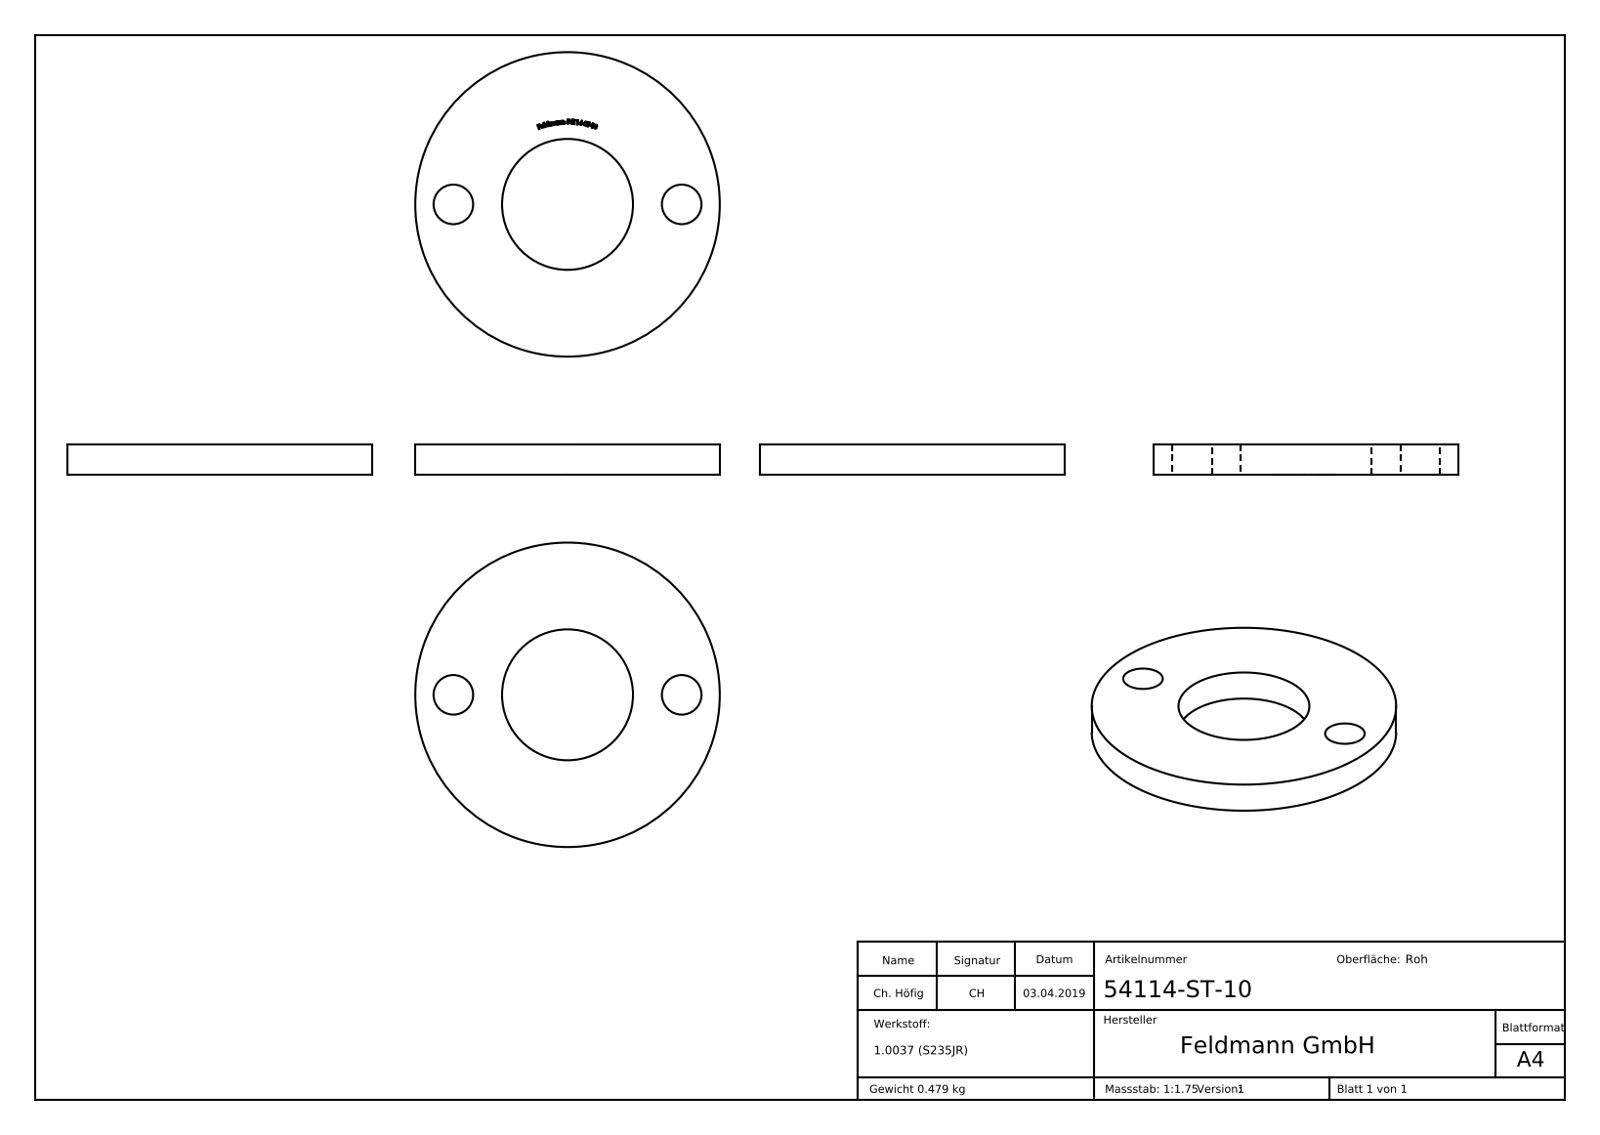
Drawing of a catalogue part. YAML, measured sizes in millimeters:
part_name: "54114-ST-10"
step_written_by: "SolidWorks 2015 (CONFIG_CONTROL_DESIGN)"
units: millimeters
bodies: {solids: 1, faces: 237, planar: 149, cylindrical: 8, other: 80}
overall_size: [100, 100, 10]
volume: 61363
surface_area: 17591
round_holes:
  - {diameter: 13, count: 2}
  - {diameter: 43, count: 1}
round_bosses_or_shafts:
  - {diameter: 100, count: 1}
face_to_face_distances: [10, 9.9, 0.73, 0.54, 0.67, 0.6, 0.72, 0.66, 1.33, 1.46]
hole_center_spacings: [37.5, 75]
